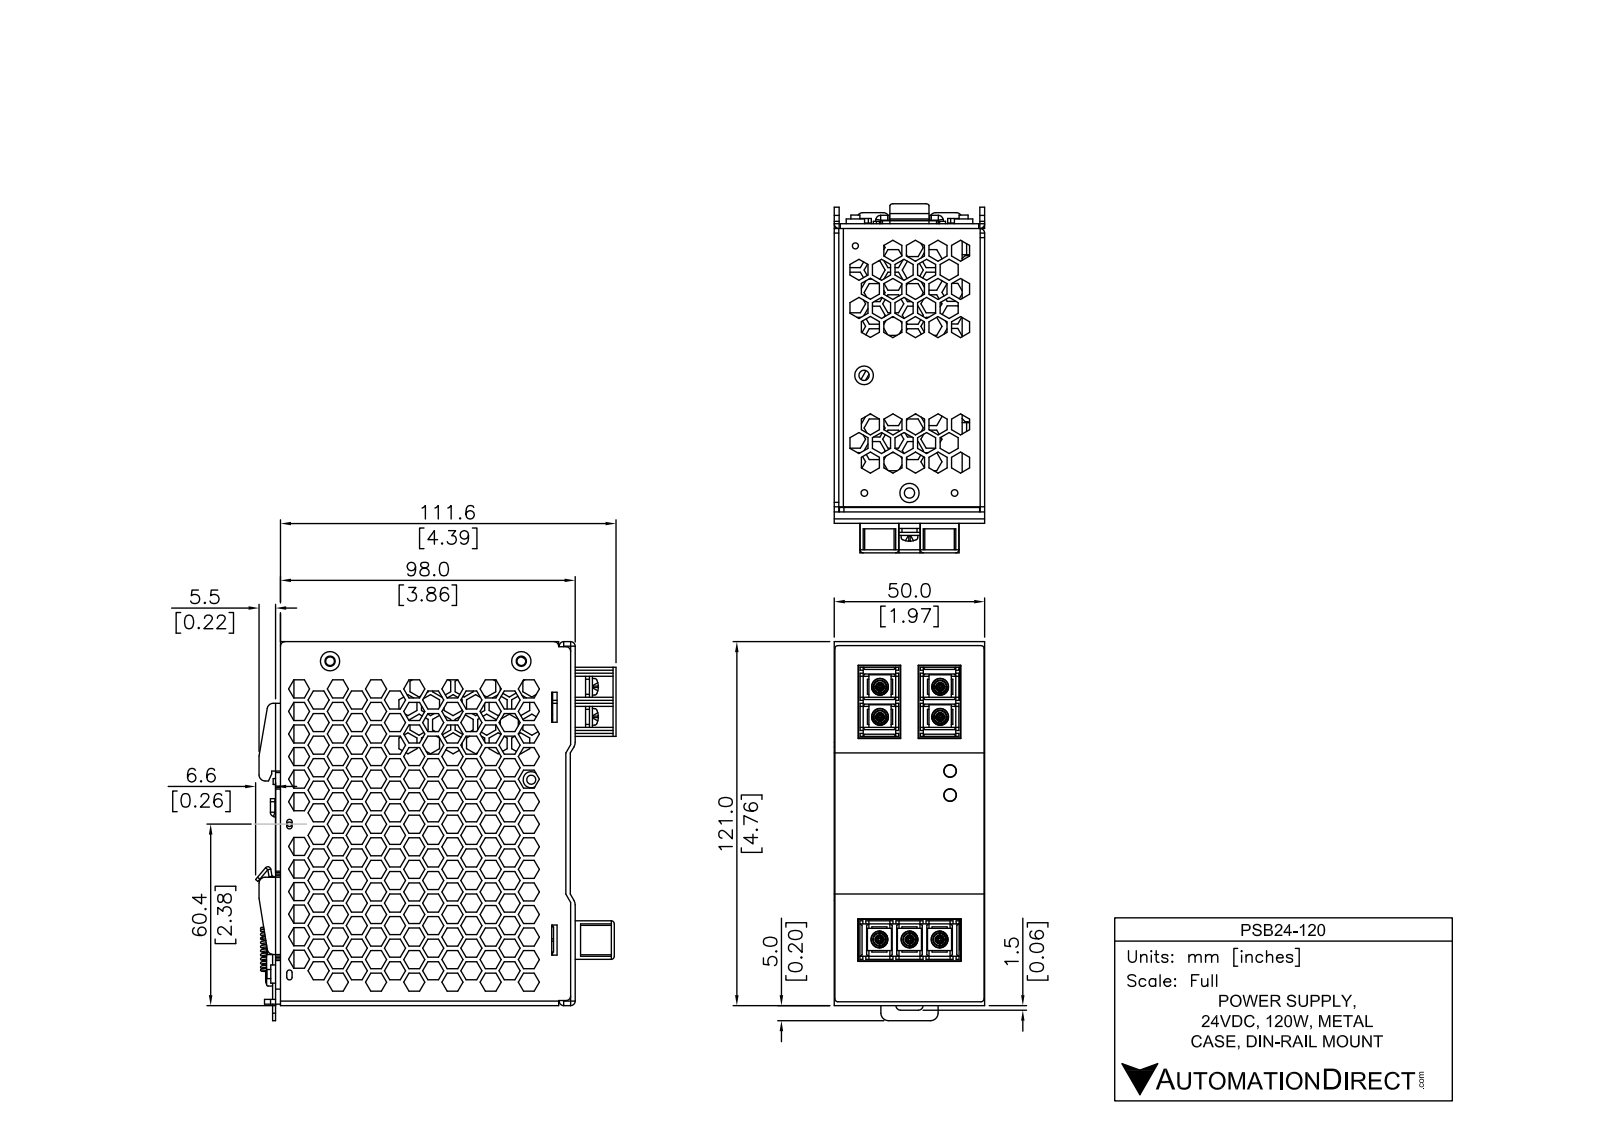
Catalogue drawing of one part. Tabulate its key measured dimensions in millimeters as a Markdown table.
| quantity | value |
| --- | --- |
| part name | PSB24-120 |
| STEP written by | SolidWorks 2011 (CONFIG_CONTROL_DESIGN) |
| units | millimeters |
| bodies | 1 solid, 3540 faces (3357 planar, 103 cylindrical, 80 other) |
| overall size | 125.6 × 117.1 × 50 |
| volume | 419 700 mm³ |
| surface area | 118 500 mm² |
| round holes (diameter × count) | 3.7 × 2 |
| round bosses / shafts (diameter × count) | 5.8 × 4, 3.2 × 4, 5.2 × 3 |
| partial cylindrical surfaces (radius × count) | 1.5 × 24, 0.8 × 13, 1.3 × 6, 1 × 3, 1 × 2, 1.9 × 2, 3.3 × 2, 0.3 × 1 |
| main face-to-face distances | 9, 41, 7.1, 1.9, 48.1, 39.1, 32, 1.5, 1.9, 49.9 |
| hole center spacings | 7.6 |
